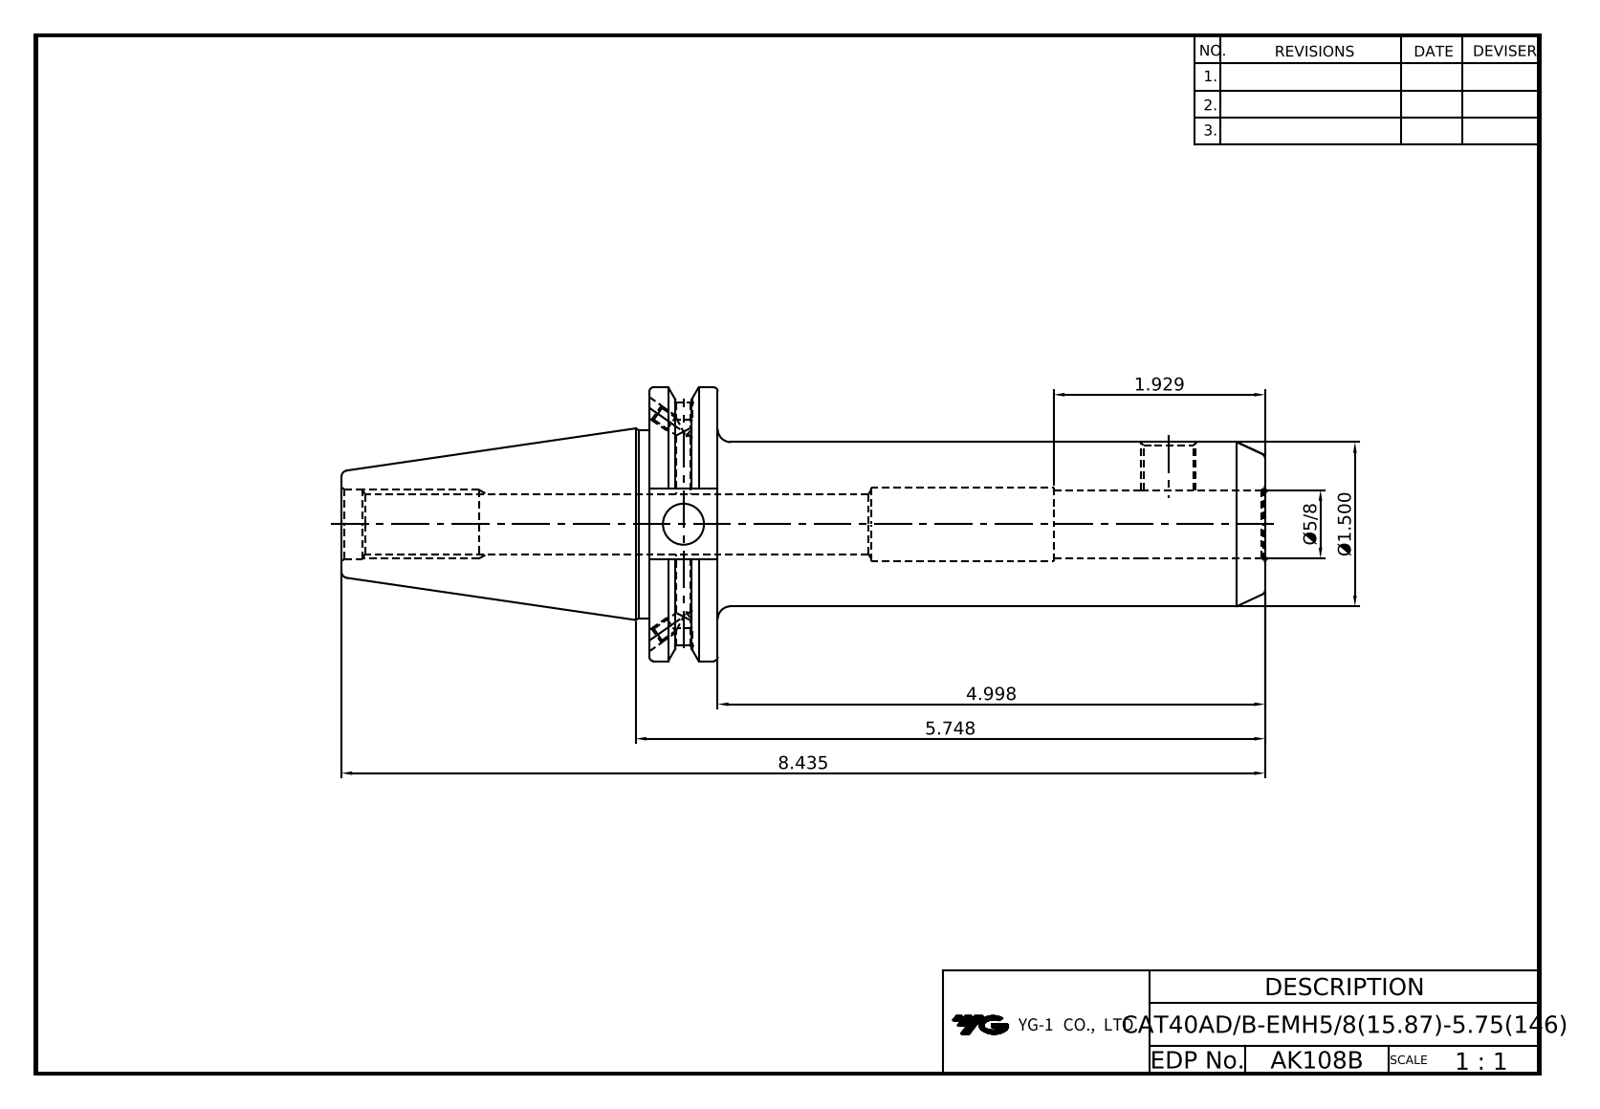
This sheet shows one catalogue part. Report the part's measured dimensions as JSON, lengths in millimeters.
{"part_name": "LO-CAT40ADB-EMH15.875-146", "step_written_by": "Autodesk Inventor 2025 (AUTOMOTIVE_DESIGN)", "units": "millimeters", "bodies": {"solids": 1, "faces": 87, "planar": 37, "cylindrical": 28, "other": 22}, "overall_size": [214.25, 63.5, 61.09], "volume_mm3": 218819, "surface_area_mm2": 41950, "round_holes": [[3.24, 4], [4, 2], [4.2, 2], [9.53, 1], [11.33, 1], [13.39, 1], [15.88, 1], [16.3, 1], [16.47, 1]], "round_bosses_or_shafts": [[63.5, 1], [43.6, 1], [38.1, 1]], "partial_cylinders_radius": [[28.15, 1]], "face_to_face_distances": [15.88, 142.83, 126.95, 47.6, 16.38, 71.42, 87.3, 214.25, 77.47, 6.05]}
